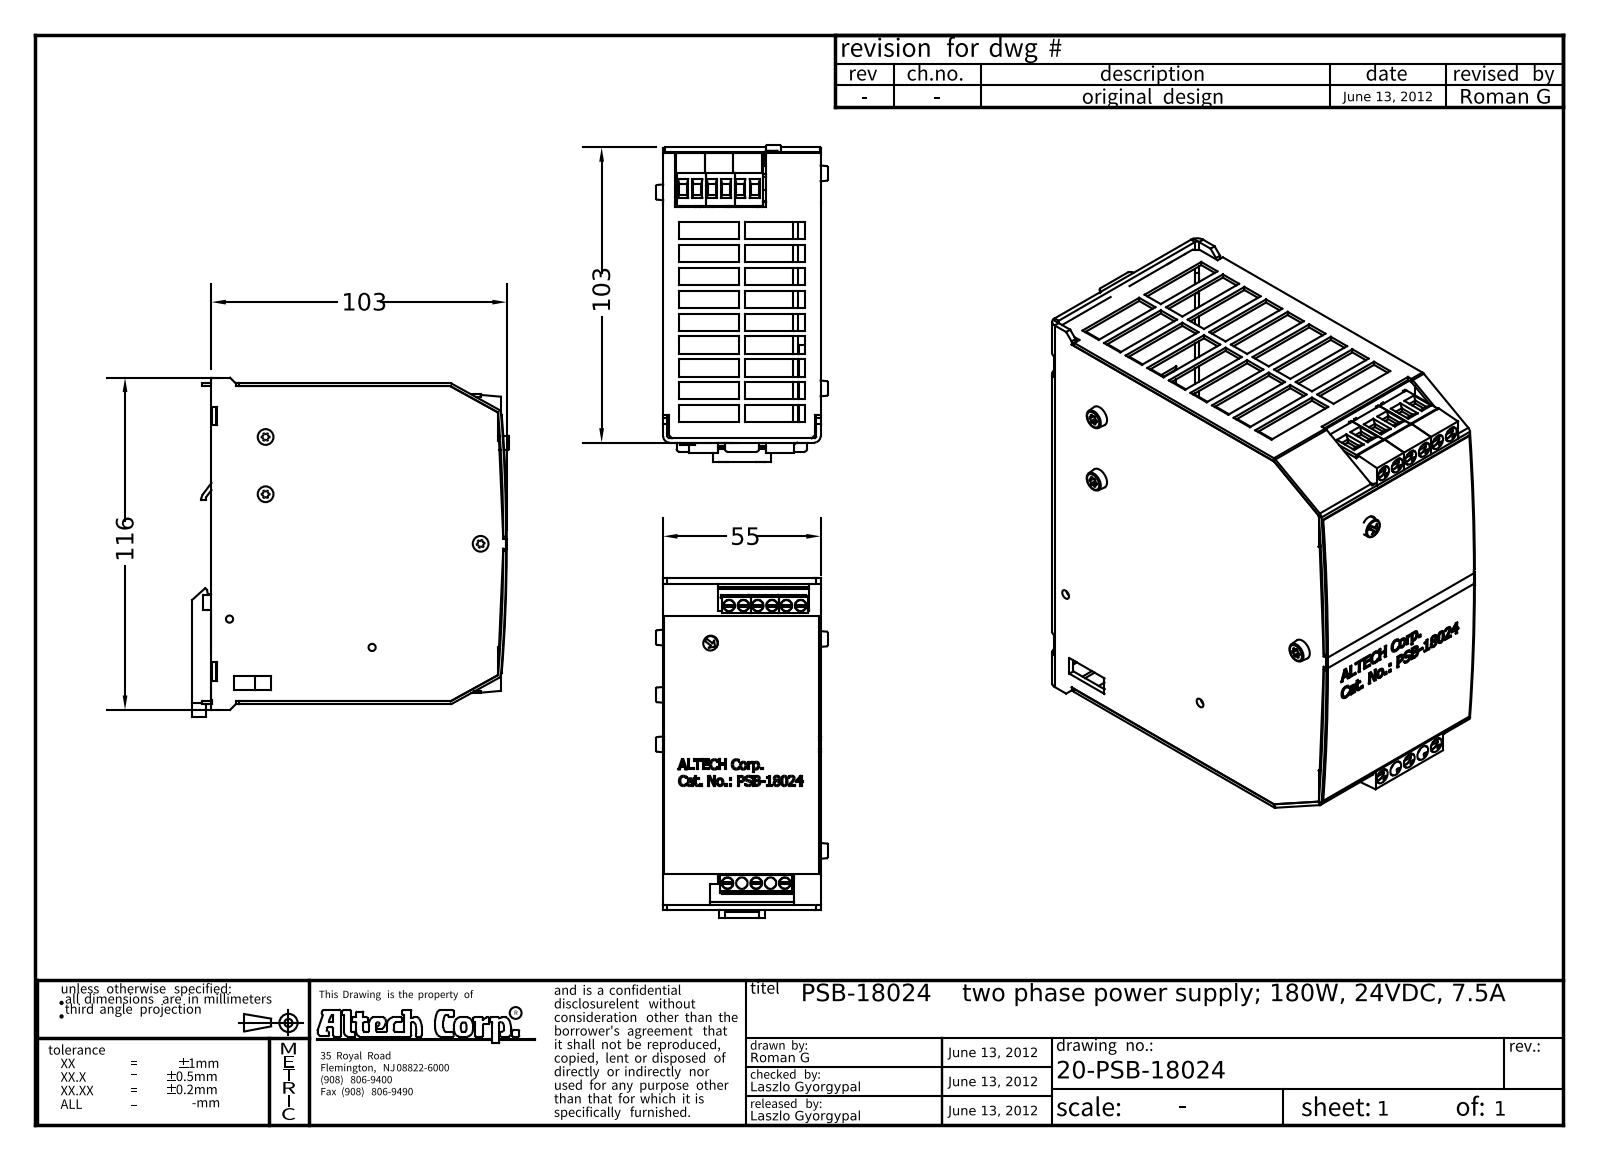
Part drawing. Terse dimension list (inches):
name: ALTECH-PSB-18024
written by: Autodesk Inventor 2013 (CONFIG_CONTROL_DESIGN)
unit: in
bodies: 1 solid, 2151 faces (1519 planar, 400 cylindrical, 232 other)
size: 4.671 × 4.354 × 2.354
volume: 5.765 in³; area: 183.7 in²
holes: 38× ⌀0.039, 11× ⌀0.157, 4× ⌀0.035, 4× ⌀0.091, 3× ⌀0.11, 3× ⌀0.13, 2× ⌀0.079, 2× ⌀0.098, 2× ⌀0.122
bosses: 9× ⌀0.152, 9× ⌀0.055, 5× ⌀0.118, 5× ⌀0.105, 2× ⌀0.185, 2× ⌀0.06, 1× ⌀0.354, 1× ⌀0.197
rounds: 46× R0.004, 31× R0.01, 30× R0.022, 17× R0.02, 16× R0.008, 12× R0.047, 8× R0.039, 8× R0.059
face distances: 0.059, 2.106, 0.063, 2.165, 0.315, 0.311, 1.795, 1.854, 0.374, 1.732
hole spacings: 0.197, 0.1, 3.716, 0.394, 0.591, 3.817, 3.821, 3.823
